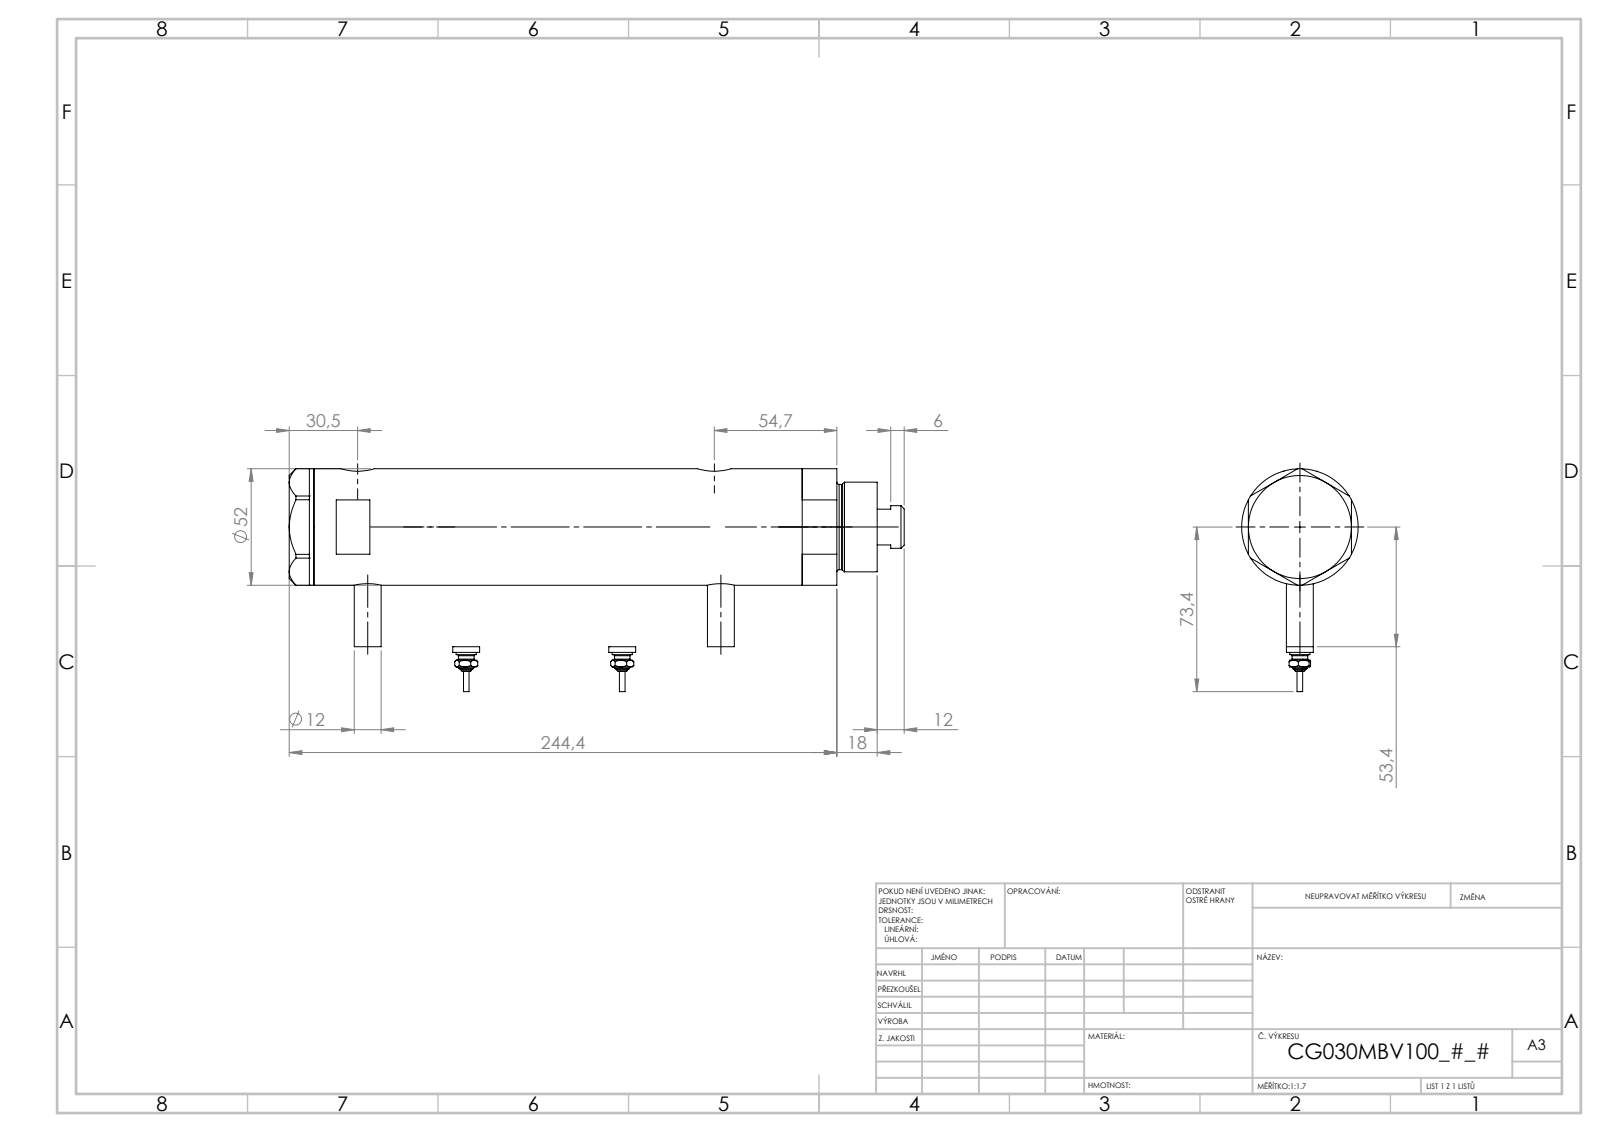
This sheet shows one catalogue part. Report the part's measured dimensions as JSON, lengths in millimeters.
{"part_name": "V270CG_VC; V270CG_FRONT; V270CG_SWITCH; V270CG_MIDDLE (+1 more)", "step_written_by": "SolidWorks 2019 (CONFIG_CONTROL_DESIGN)", "units": "millimeters", "bodies": {"solids": 6, "faces": 246, "planar": 95, "cylindrical": 77, "other": 74}, "overall_size": [249.02, 84.3, 52], "volume_mm3": 443477, "surface_area_mm2": 99080, "round_holes": [[5, 2], [9.73, 2], [12.5, 2], [15, 2], [6.5, 1], [20, 1], [21.5, 1], [30, 1], [33, 1], [44, 1]], "round_bosses_or_shafts": [[12, 3], [9, 2], [7, 2], [4.34, 2], [2.4, 2], [52, 1], [40, 1], [38, 1]], "face_to_face_distances": [153.54, 23.8, 129.74, 11, 34.8, 164.54, 46, 200.94, 189.94, 166.14], "hole_center_spacings": [2.9, 4.5, 126.75, 129.65, 131.25, 134.15, 2.89, 2.91]}
